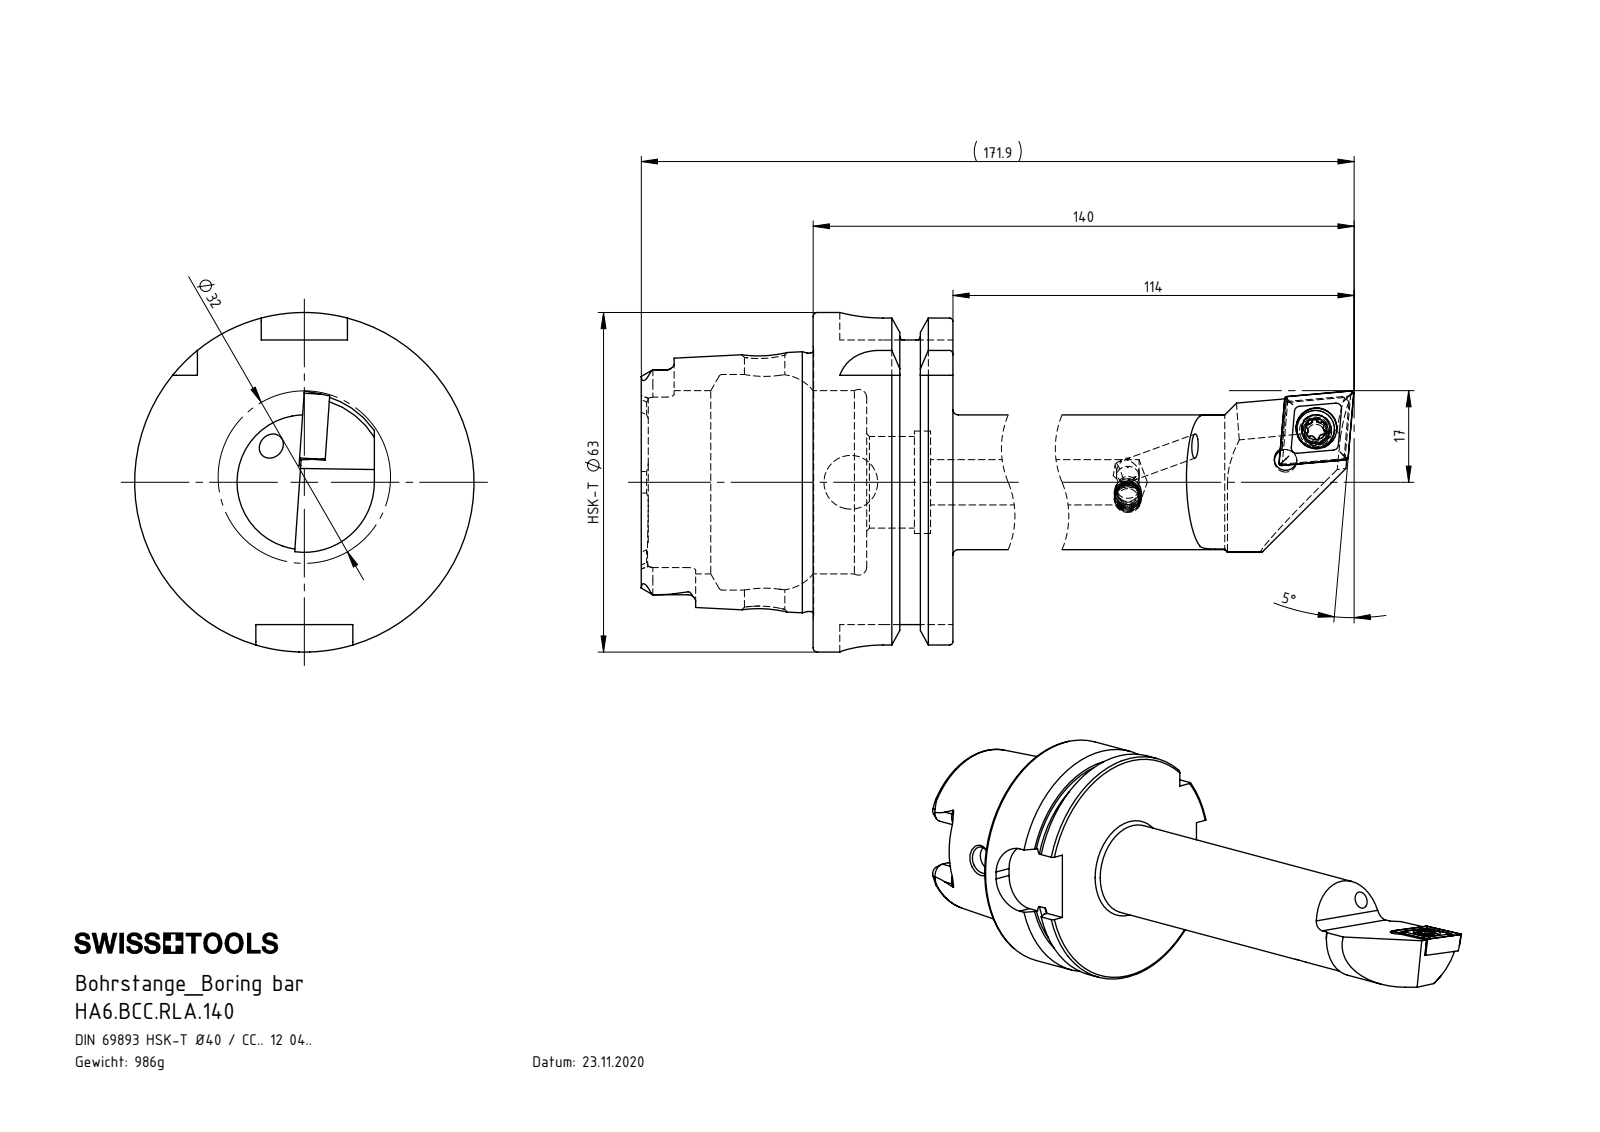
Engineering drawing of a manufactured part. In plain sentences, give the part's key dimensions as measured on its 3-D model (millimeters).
The part is named "HA6-BCC.RLA.140_A; HA6.BCC.RLA.140; WCC-ER2.001.010_A; KVT_MB_600_050 (+1 more)". Its 3-D file was written by "SolidWorks 2017 (AUTOMOTIVE_DESIGN)". It is 5 solids with 241 faces: 75 planar, 61 cylindrical and 105 other. Overall it measures 171.86 by 63 by 63 millimeters. Its volume is 125 677 cubic millimeters and its surface area 34 012 square millimeters. Round holes: 4 of diameter 4.2, 1 of diameter 4, 1 of diameter 5, 1 of diameter 5.5, 1 of diameter 7.5, 1 of diameter 7.6, 1 of diameter 8.4, 1 of diameter 10, 1 of diameter 17, 1 of diameter 19, 1 of diameter 34, 1 of diameter 40. Round bosses or shafts: 2 of diameter 5, 1 of diameter 63, 1 of diameter 54.95, 1 of diameter 47.94, 1 of diameter 25, 1 of diameter 7. Partial cylindrical surfaces (rounded edges, fillets, slot ends): 6 of radius 0.39, 6 of radius 1.4, 4 of radius 2.88, 4 of radius 8, 3 of radius 0.69, 3 of radius 0.69, 1 of radius 3, 1 of radius 13. The main face-to-face distances are 25.95, 16, 9.95, 31.9, 41.85, 57.85, 52.8, 21.8, 11.85, 53.7. The hole center spacings are 7.89, 8.09.
